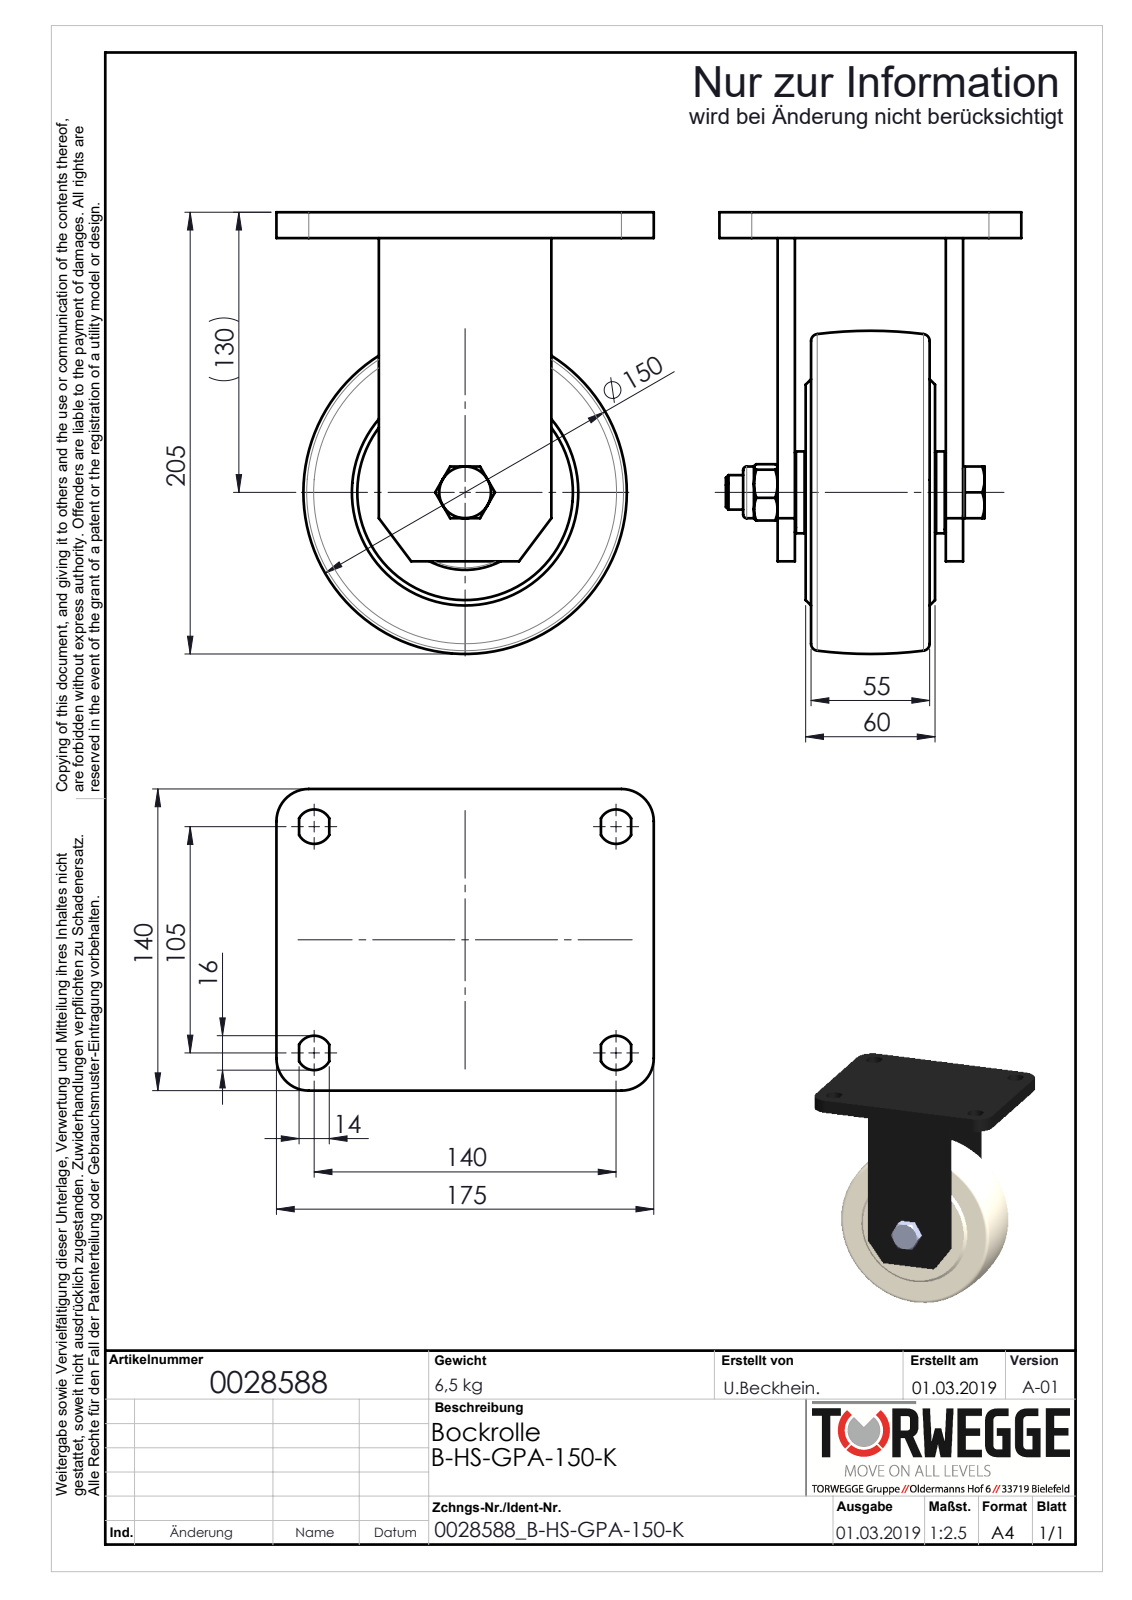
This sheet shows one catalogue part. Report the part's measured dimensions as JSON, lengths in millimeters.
{"part_name": "0028588_B-HS-GPA-150-K_(A-01)", "step_written_by": "SolidWorks 2018 (AUTOMOTIVE_DESIGN)", "units": "millimeters", "bodies": {"solids": 0, "faces": 199, "planar": 63, "cylindrical": 60, "other": 76}, "overall_size": [205, 175, 140], "round_holes": [[14, 1], [16, 1], [16.3, 1], [18.29, 1], [30, 1], [31, 1], [58.3, 1], [72, 1]], "round_bosses_or_shafts": [[43.7, 1], [38, 1], [24, 1]], "partial_cylinders_radius": [[8, 4], [15, 4]], "face_to_face_distances": [8, 78, 12, 15.5, 70.5, 7.5, 62.5, 70, 13, 73]}
